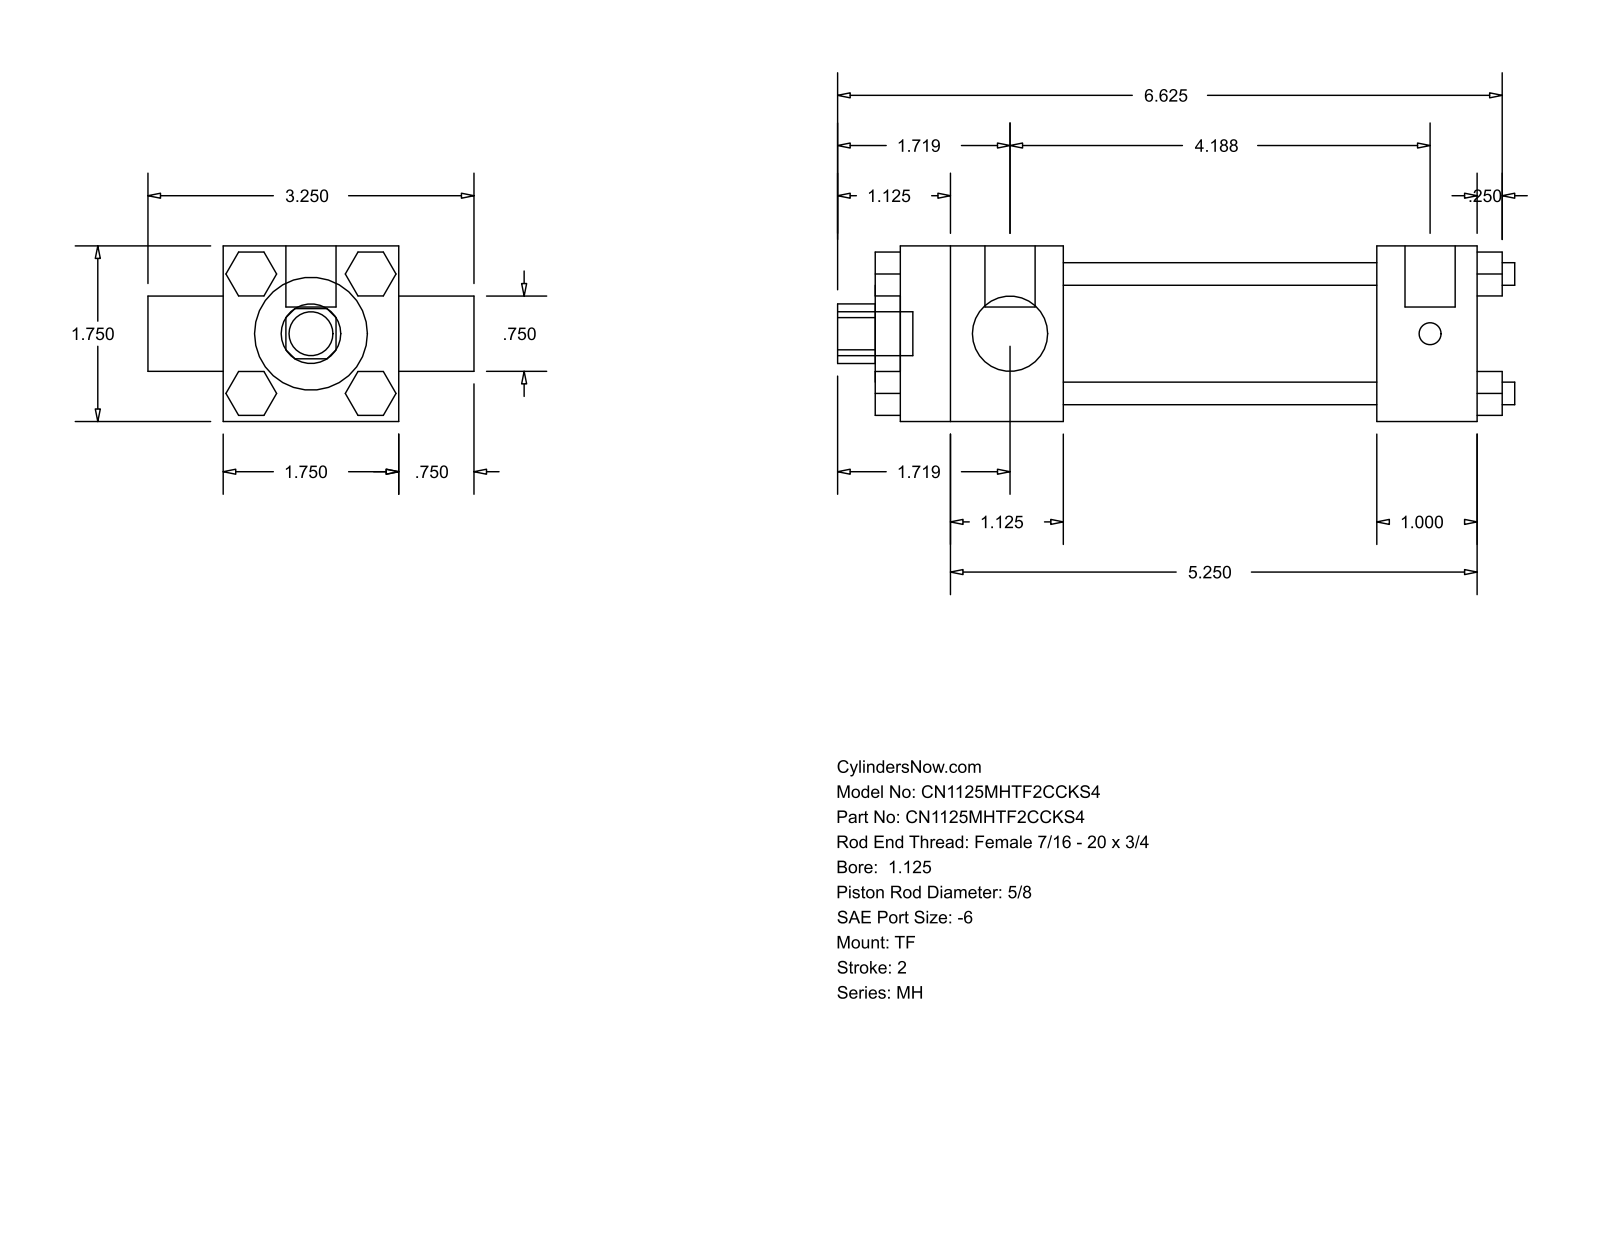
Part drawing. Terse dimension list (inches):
name: MH_TF__0112_0.625
written by: GSSL Pune (CONFIG_CONTROL_DESIGN)
unit: in
bodies: 0 solids, 120 faces (92 planar, 28 cylindrical, 0 other)
size: 6.75 × 3.25 × 1.75
holes: 1× ⌀0.625, 1× ⌀0.75, 1× ⌀1.125, 1× ⌀1.375
bosses: 4× ⌀0.225, 3× ⌀0.219, 2× ⌀0.5, 1× ⌀0.437
rounds: 1× R0.297
face distances: 1.75, 6, 0.25, 0.437, 3.125, 4.125, 1, 1.625, 4.75, 5.75
